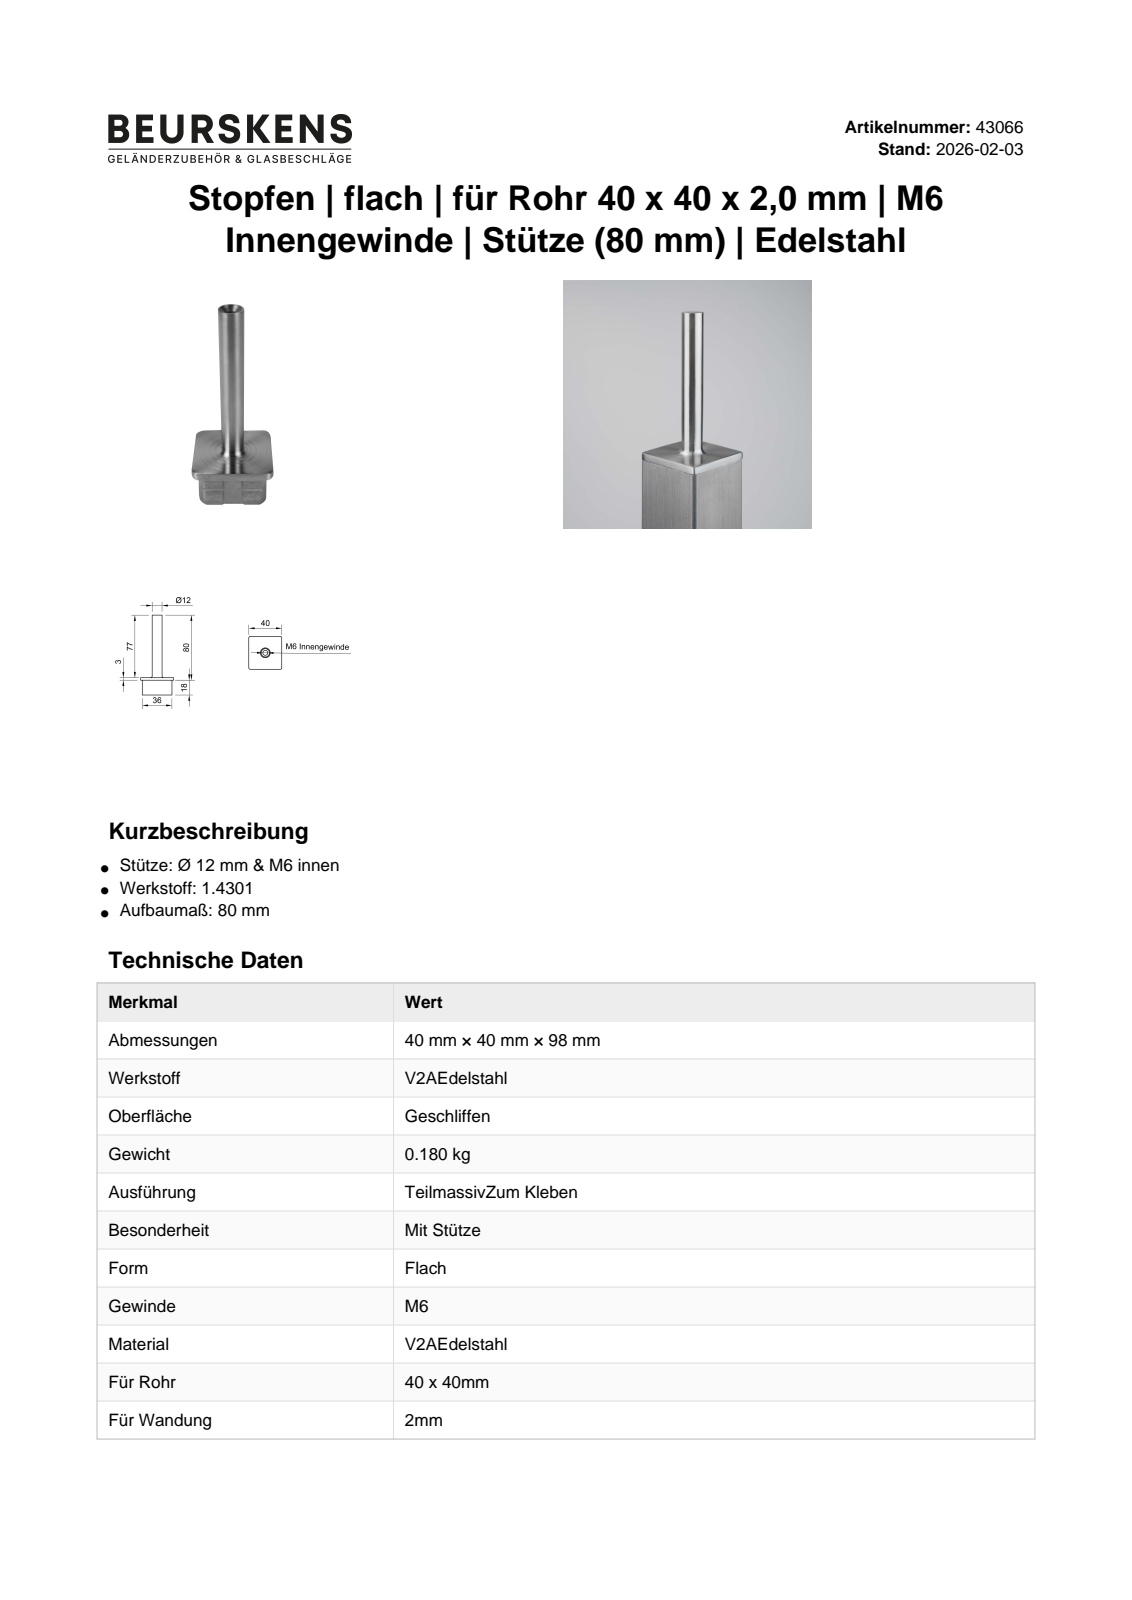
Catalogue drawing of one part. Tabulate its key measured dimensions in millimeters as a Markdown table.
| quantity | value |
| --- | --- |
| part name | 43066 |
| STEP written by | Autodesk Inventor 2022 (AUTOMOTIVE_DESIGN) |
| units | millimeters |
| bodies | 2 solids, 37 faces (22 planar, 13 cylindrical, 2 other) |
| overall size | 97 × 40 × 40 |
| volume | 17 379 mm³ |
| surface area | 12 699 mm² |
| round holes (diameter × count) | 6 × 1, 8 × 1 |
| round bosses / shafts (diameter × count) | 12 × 1, 11 × 1 |
| partial cylindrical surfaces (radius × count) | 2 × 8 |
| main face-to-face distances | 2, 34, 36, 32, 4, 38, 1, 3, 18, 19 |
